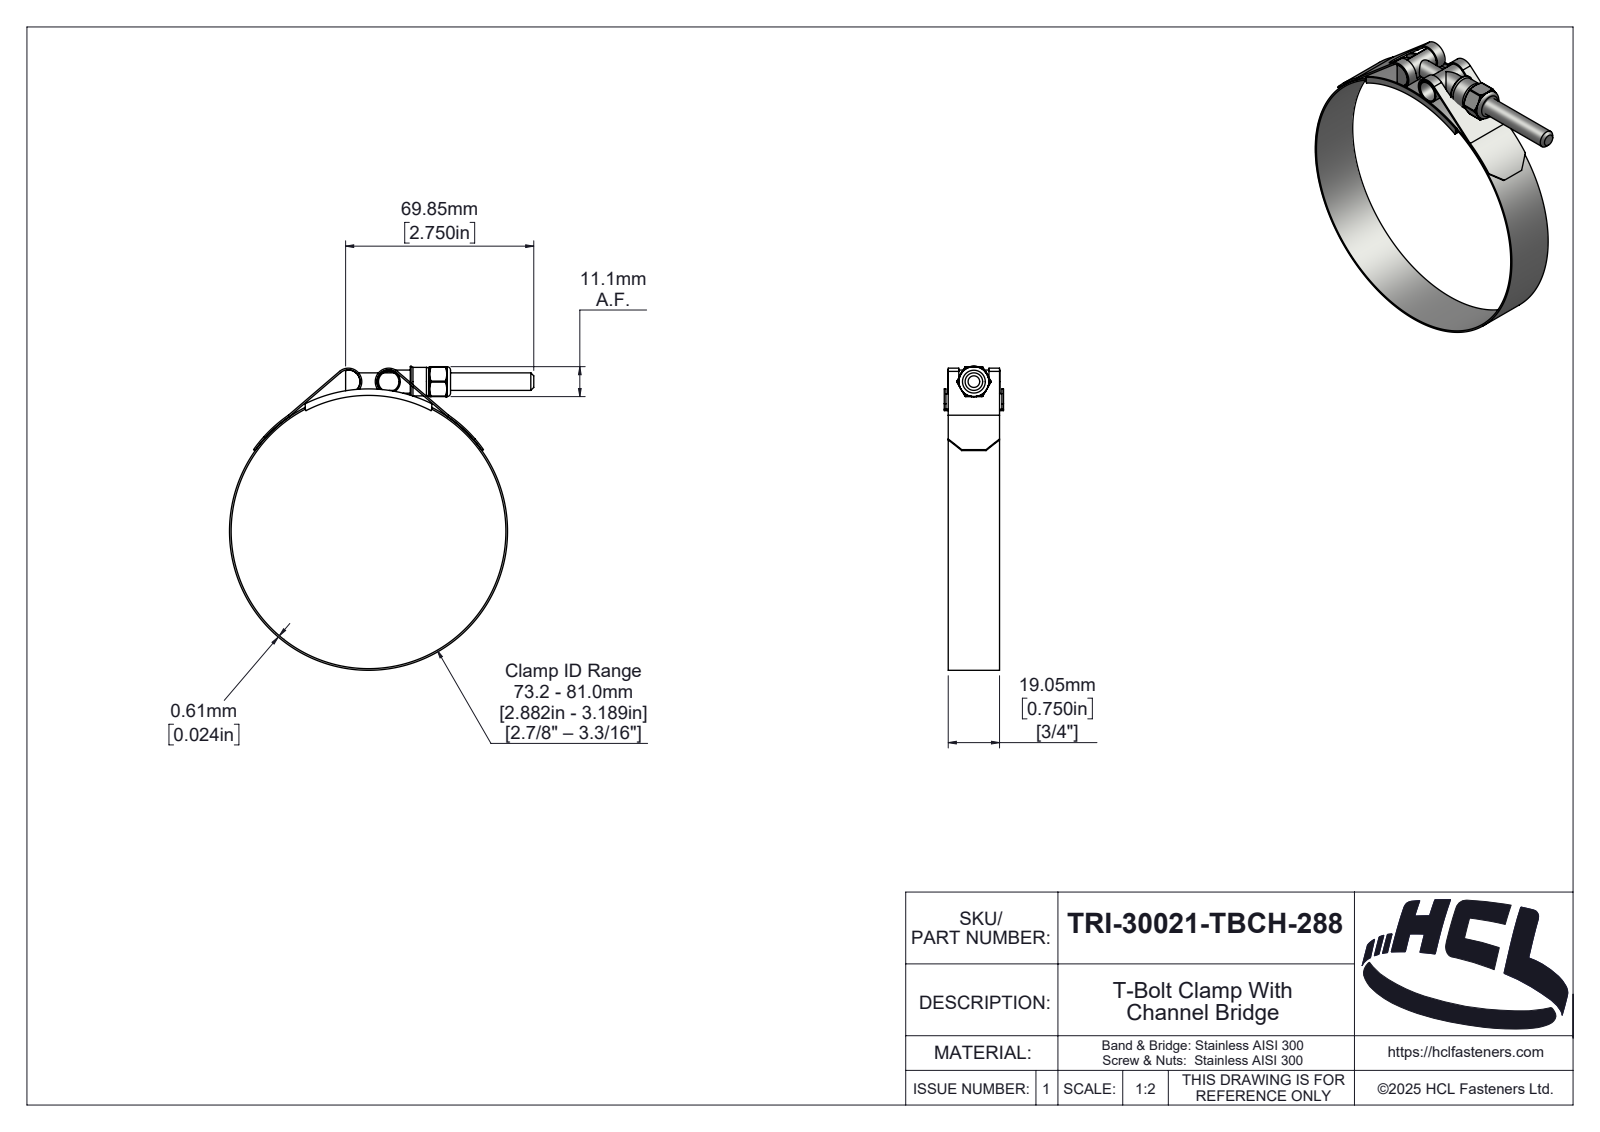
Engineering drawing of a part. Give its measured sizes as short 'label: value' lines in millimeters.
name: TRI-30021-TBCH-288
written by: SolidWorks 2025 (AUTOMOTIVE_DESIGN)
unit: mm
bodies: 6 solids, 330 faces (46 planar, 122 cylindrical, 162 other)
size: 112.96 × 112.83 × 22
volume: 9 554 mm³; area: 22 652 mm²
holes: 1× ⌀5.4, 1× ⌀6.35, 1× ⌀6.5, 1× ⌀7.58, 1× ⌀102
bosses: 2× ⌀8.58, 1× ⌀103.22, 1× ⌀10.58
rounds: 6× R0.39, 2× R0.5, 2× R4.39, 2× R5, 1× R0.59, 1× R2.42, 1× R3.03, 1× R3.19
face distances: 0.61, 19.06, 1.47, 20.53, 21.39, 0.86, 19.92, 0.74, 22, 11.11
hole spacings: 56
